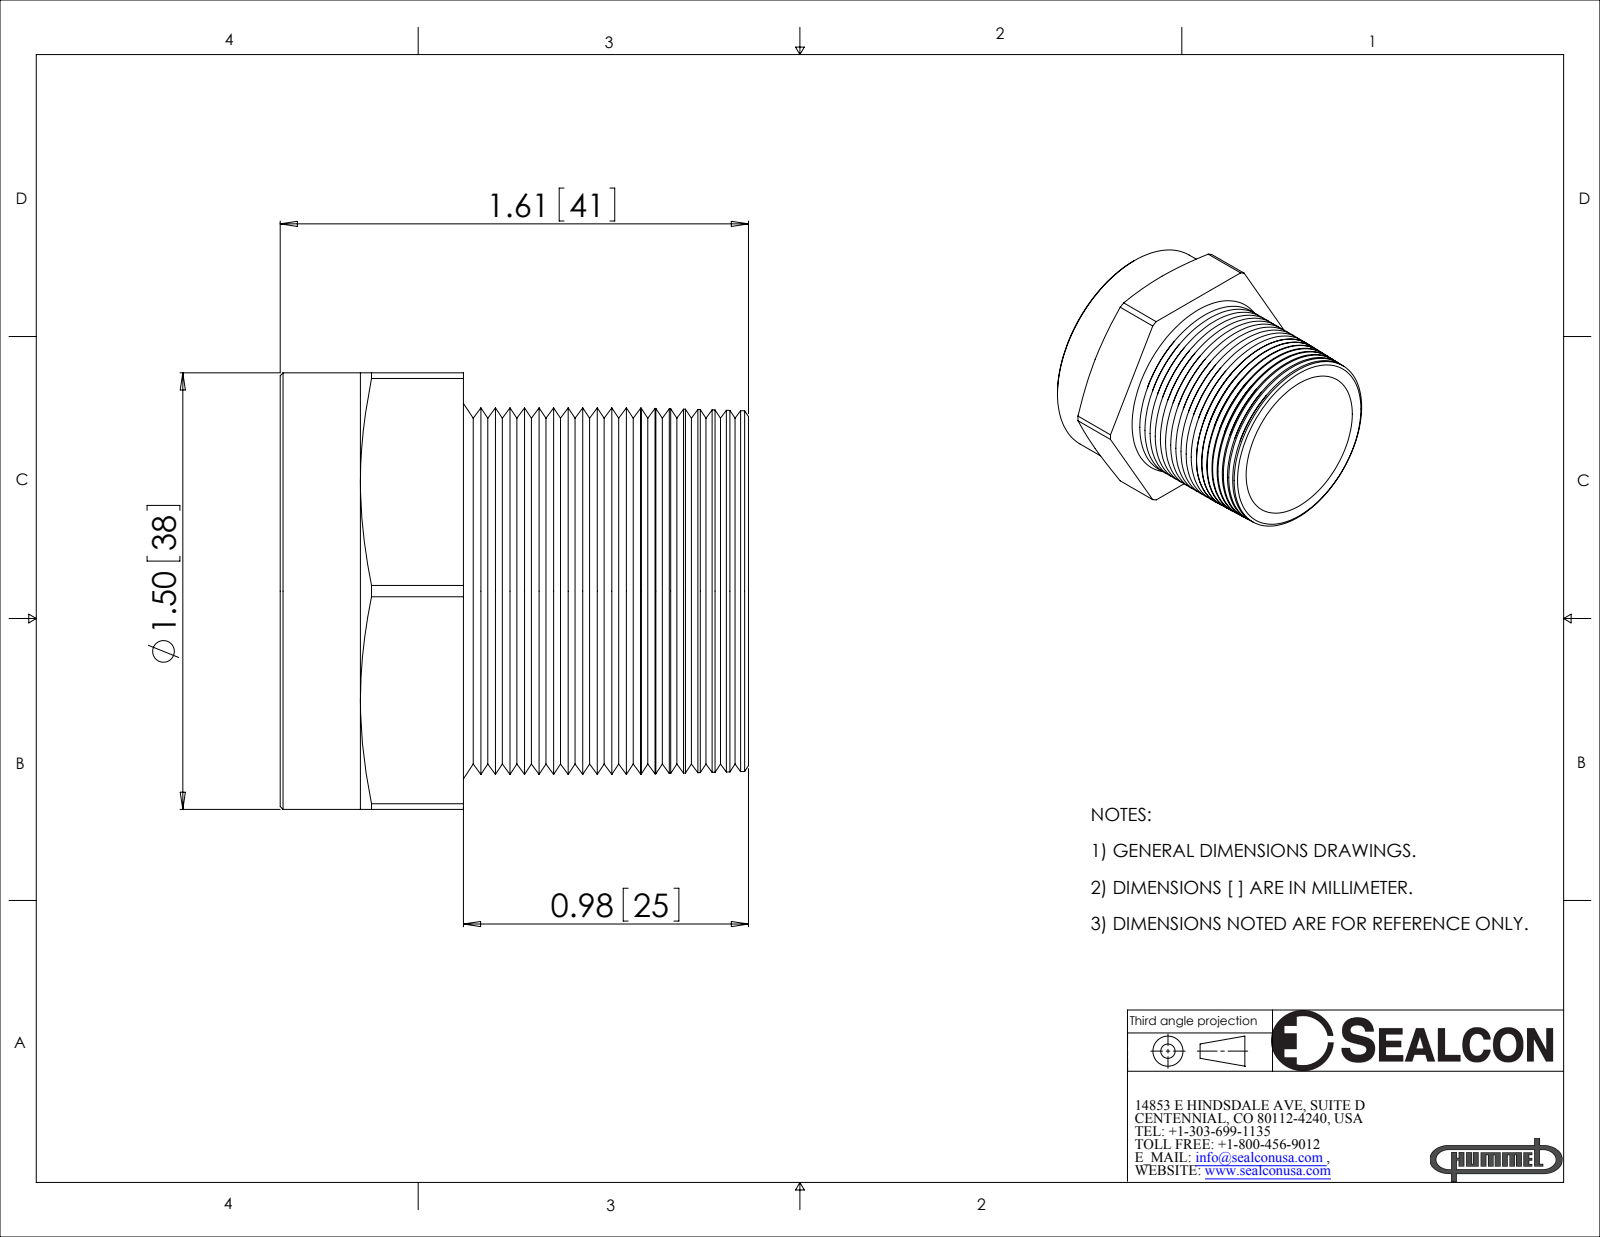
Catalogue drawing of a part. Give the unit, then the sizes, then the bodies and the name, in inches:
Units: inches
Overall size (bounding box): 1.71 × 1.61 × 1.5
Round holes (diameter × count): ⌀1.032 ×1, ⌀1.304 ×1
Round bosses / shafts (diameter × count): ⌀1.5 ×1
Partial cylindrical surfaces — rounded edges, fillets, slot ends (radius × count): R0.855 ×1
Main face-to-face distances: 1.5, 0.63, 0.081, 0.549, 0.98, 1.061, 1.61, 1.222, 0.242, 0.161
Volume: 0.773 in³ · Surface area: 18.63 in²
Bodies: 1 solid, 159 faces (11 planar, 13 cylindrical, 135 other)
Part name (STEP PRODUCT): AT-1032-BR
STEP written by: SolidWorks 2008 (CONFIG_CONTROL_DESIGN)
